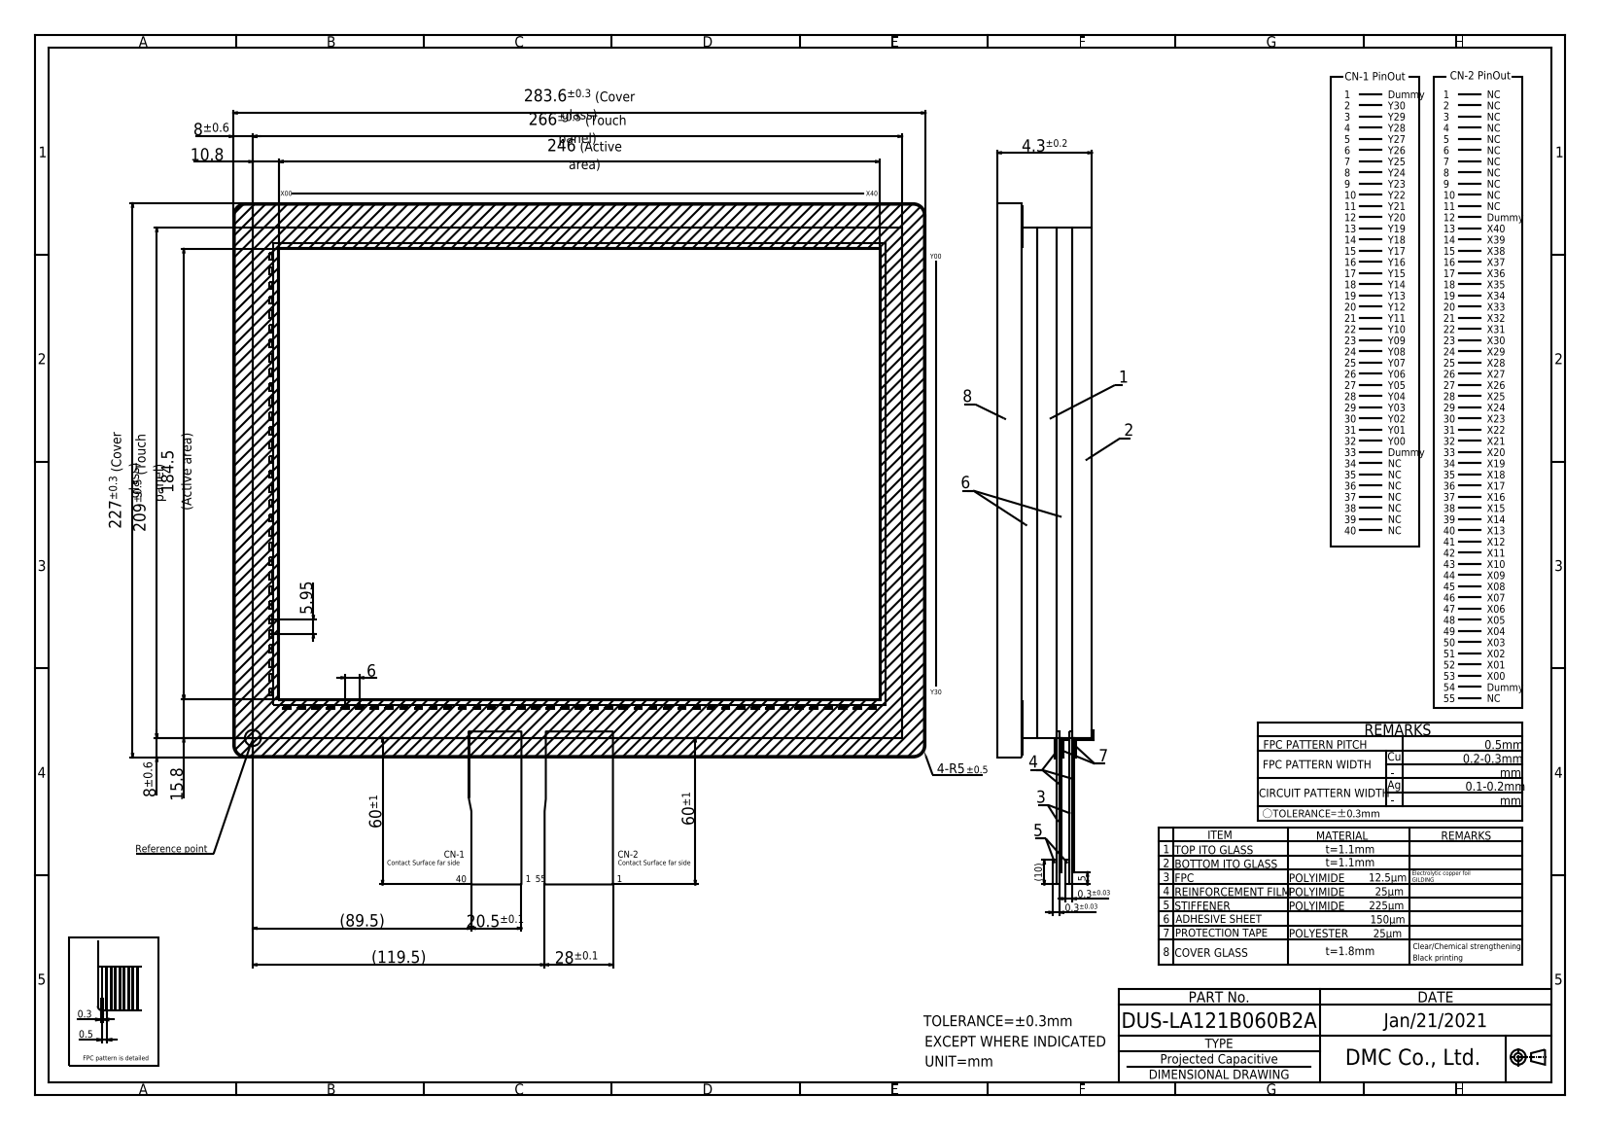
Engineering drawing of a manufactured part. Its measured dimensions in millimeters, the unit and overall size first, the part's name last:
Units: millimetres
Overall size (bounding box): 397.04 × 324.4 × 4.3
Partial cylindrical surfaces — rounded edges, fillets, slot ends (radius × count): R5 ×4, R0.2 ×1
Main face-to-face distances: 4.3, 1.8, 2.5, 2.4, 1.9, 1.25, 1.15, 1.35, 3.15, 3.05
Volume: 250 699 mm³ · Surface area: 229 689 mm²
Bodies: 1 solid, 425 faces (420 planar, 5 cylindrical, 0 other)
Part name (STEP PRODUCT): DUS-LA121B060B2A
STEP written by: Autodesk Inventor 2020 (CONFIG_CONTROL_DESIGN)
